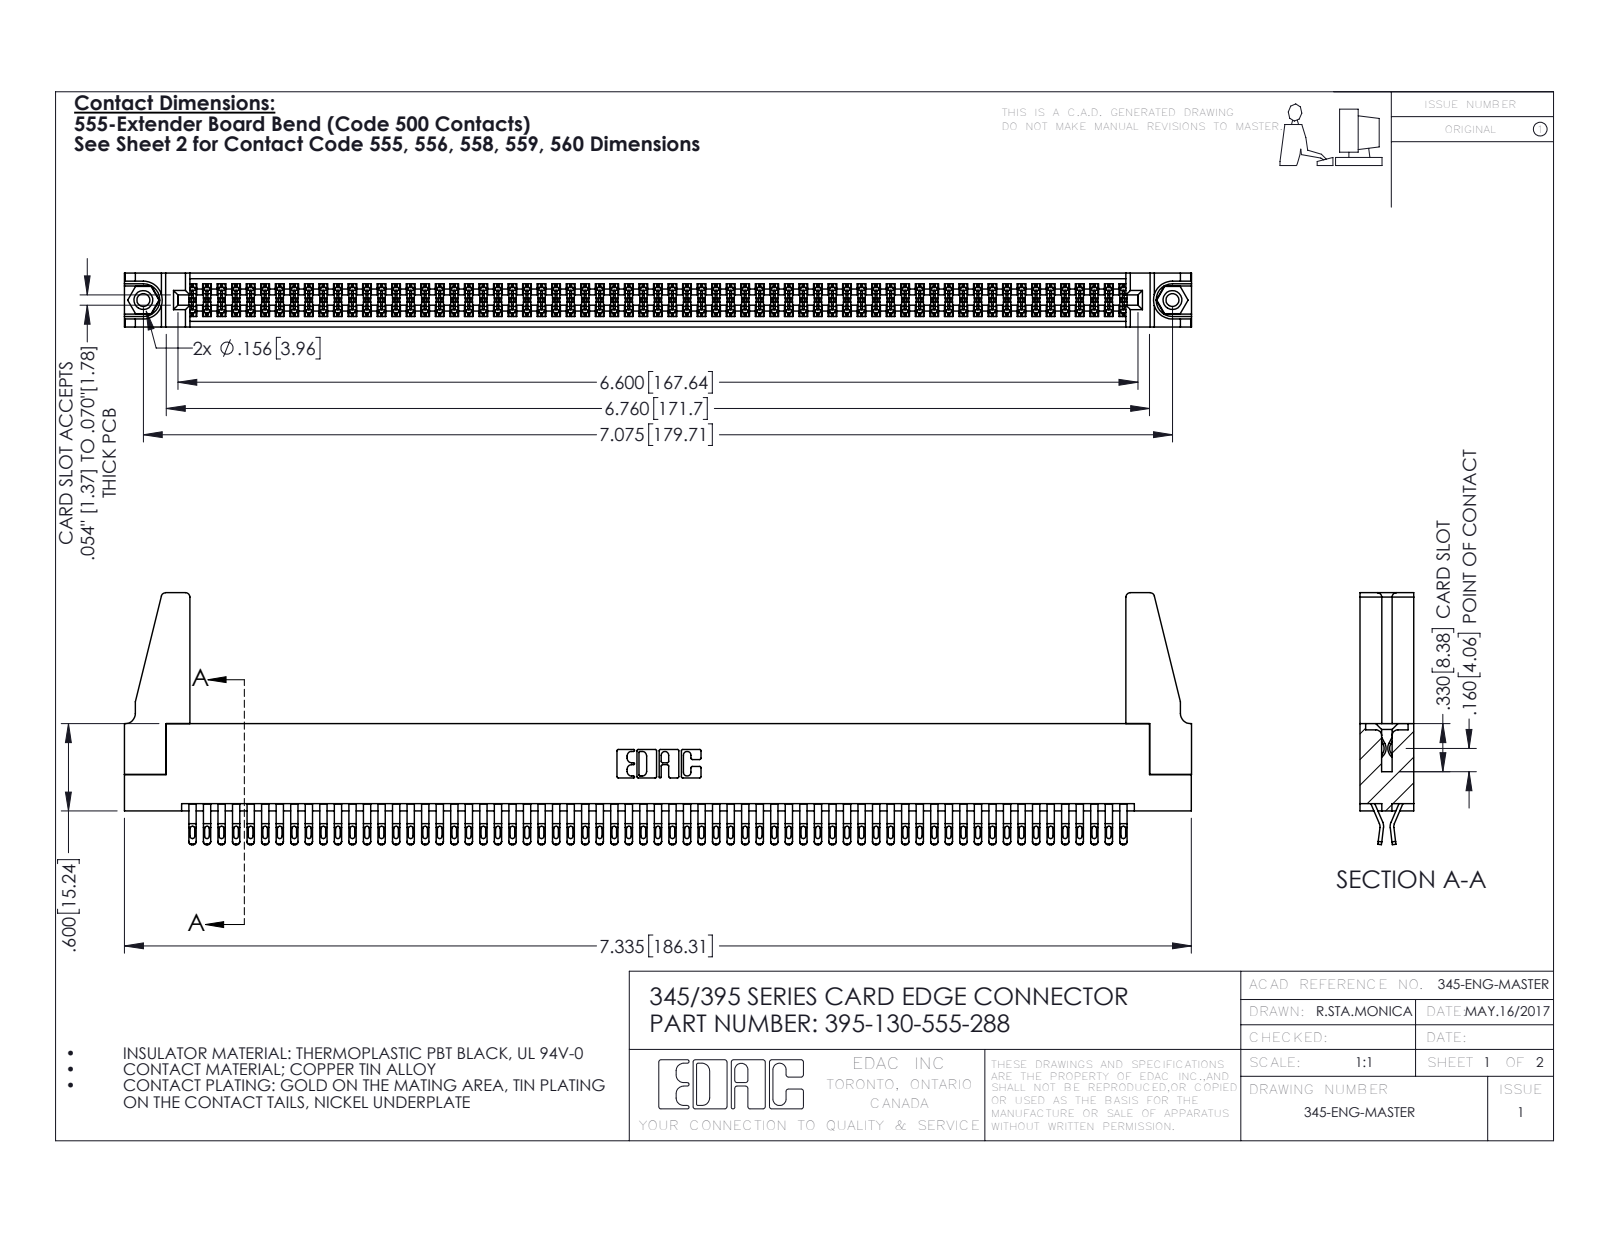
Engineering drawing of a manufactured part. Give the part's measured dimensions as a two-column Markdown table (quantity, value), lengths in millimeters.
| quantity | value |
| --- | --- |
| part name | 395-130-555-288; 345 Part_Flush Mounting Lugs - 0.156 Dia-TH; 345-292-001_555 Tail; 345-220-078_345-220-088 (+1 more) |
| STEP written by | SolidWorks 2016 (CONFIG_CONTROL_DESIGN) |
| units | millimeters |
| bodies | 135 solids, 7530 faces (4182 planar, 3332 cylindrical, 16 other) |
| overall size | 186.3 × 44 × 9.4 |
| volume | 21 940 mm³ |
| surface area | 32 510 mm² |
| round holes (diameter × count) | 2.3 × 2, 3.2 × 2, 4 × 2, 1.6 × 1 |
| round bosses / shafts (diameter × count) | 3.9 × 2 |
| partial cylindrical surfaces (radius × count) | 0.4 × 325, 0.5 × 260, 0.2 × 195, 0.3 × 22, 0.8 × 8, 0.2 × 6, 0.8 × 6, 0.7 × 3 |
| main face-to-face distances | 1.8, 7.6, 9.4, 0.6, 5.1, 2.5, 6.9, 5.7, 4.4, 3.8 |
| hole center spacings | 6.9, 173.7, 179.7 |
